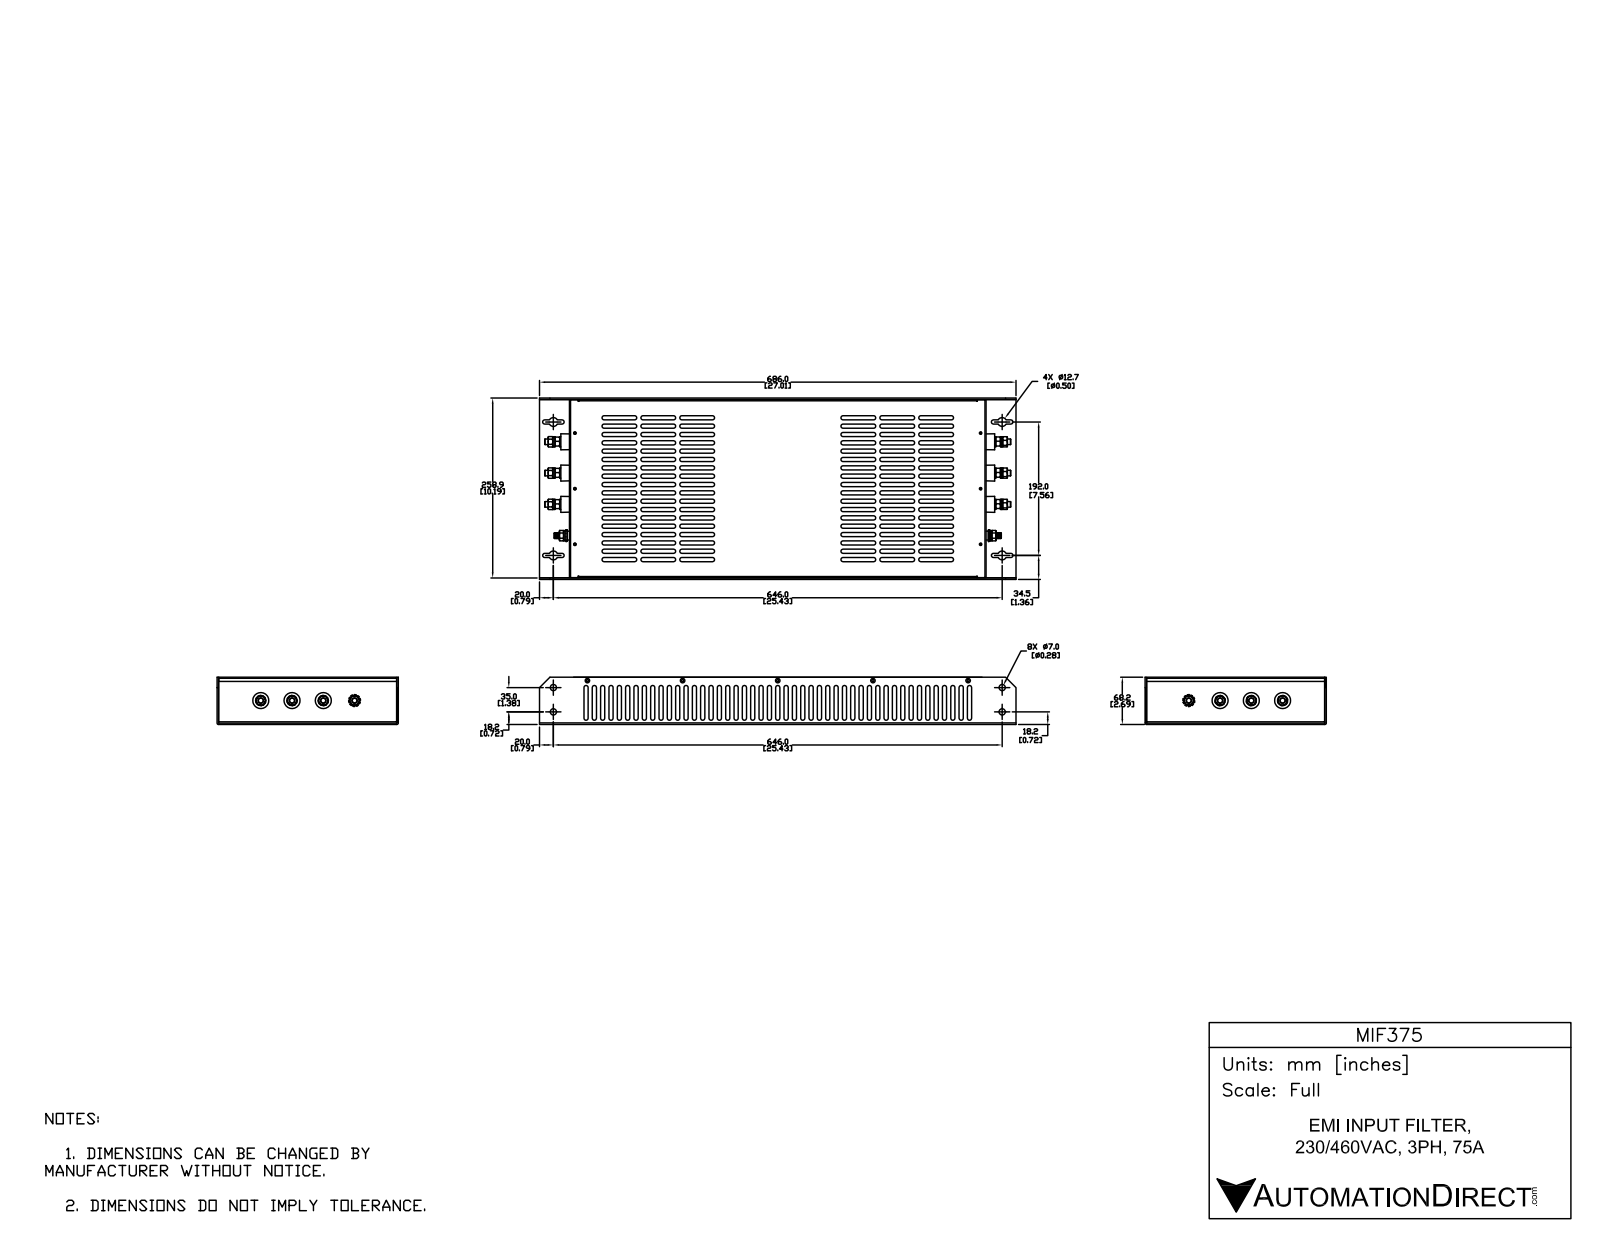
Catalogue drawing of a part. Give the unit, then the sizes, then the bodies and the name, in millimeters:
Units: millimetres
Overall size (bounding box): 686 × 260.9 × 68.2
Round holes (diameter × count): ⌀3.3 ×19, ⌀3.5 ×6, ⌀6.8 ×4, ⌀8.4 ×4, ⌀9 ×4, ⌀8 ×3, ⌀12 ×3, ⌀12.2 ×3, ⌀8.5 ×1
Round bosses / shafts (diameter × count): ⌀5.9 ×8, ⌀5 ×8, ⌀14.7 ×4, ⌀13 ×1, ⌀12.6 ×1, ⌀12.5 ×1, ⌀10.5 ×1, ⌀9.8 ×1
Partial cylindrical surfaces — rounded edges, fillets, slot ends (radius × count): R3 ×322, R0.8 ×8, R2 ×8, R3.3 ×8, R0.4 ×6, R1.6 ×4, R2.7 ×4, R2.7 ×4
Main face-to-face distances: 2, 1.2, 65, 67, 68.2, 66.2, 258.9, 256.9, 260.9, 595.2
Hole centre spacings: 80, 160, 19.5, 80, 98.3, 137, 178.2, 576.8
Volume: 761 000 mm³ · Surface area: 946 400 mm²
Bodies: 83 solids, 3646 faces (1476 planar, 1218 cylindrical, 952 other)
Part name (STEP PRODUCT): MIF375-375B r1
STEP written by: SolidWorks 2017 (AUTOMOTIVE_DESIGN)
